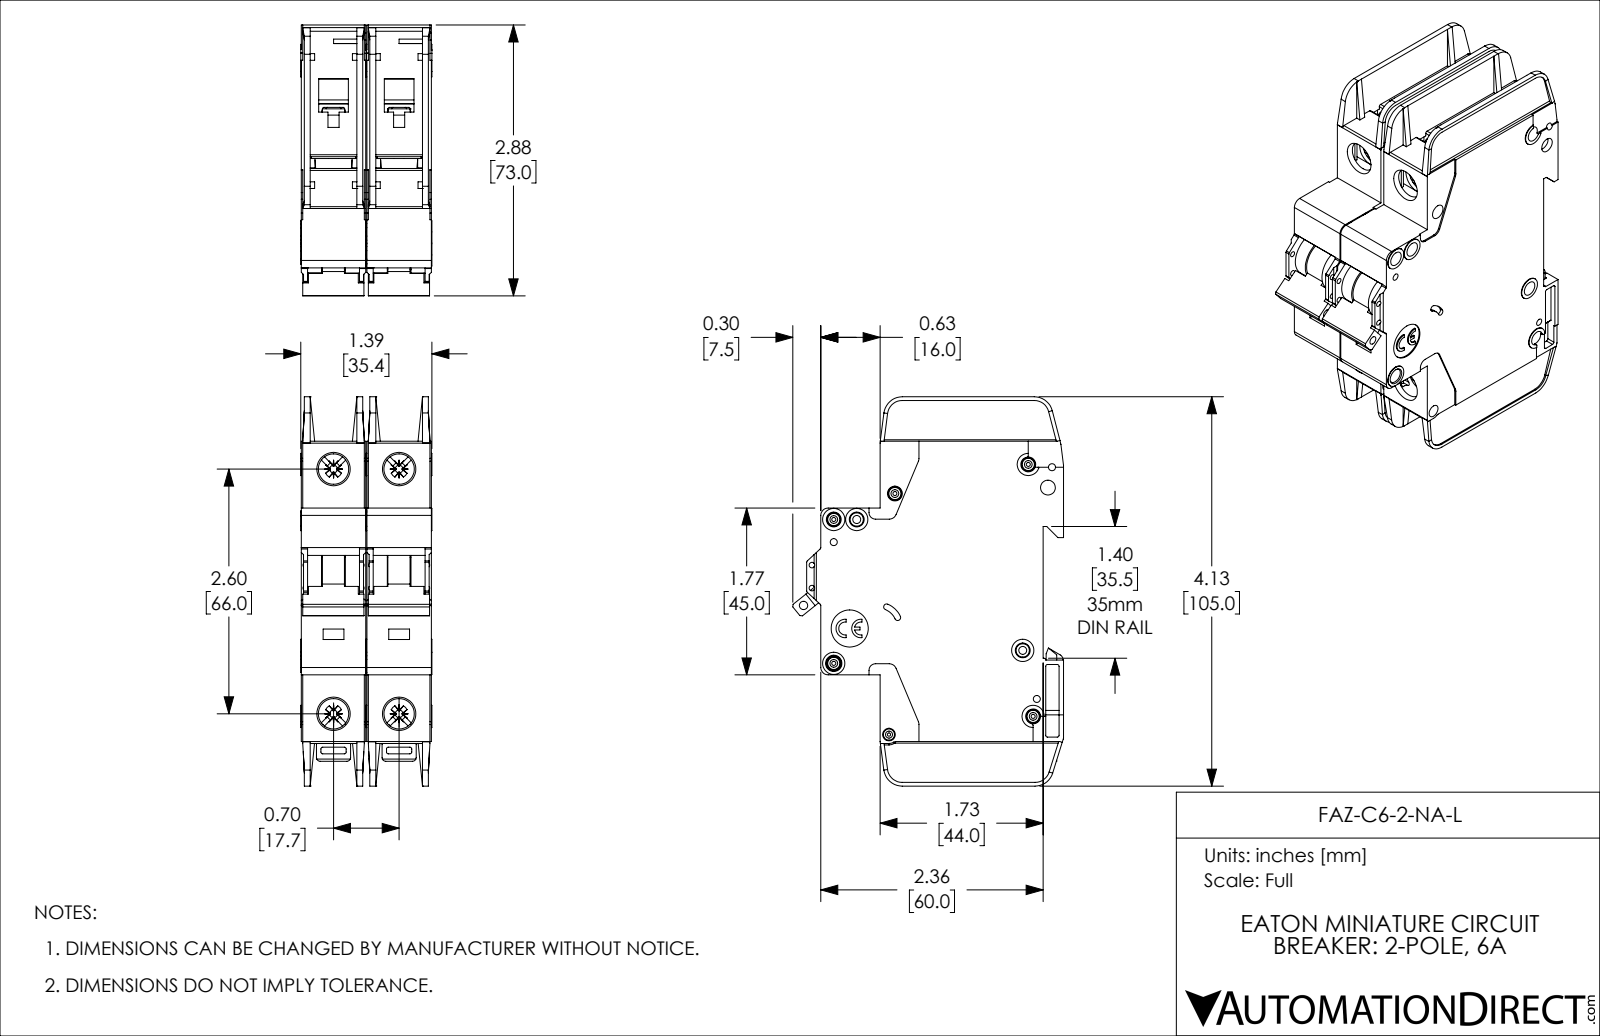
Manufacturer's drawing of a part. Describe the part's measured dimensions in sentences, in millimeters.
The part is named "FAZ-C6-2-NA-L". Its 3-D file was written by "SolidWorks 2019 (AUTOMOTIVE_DESIGN)". It is 2 solids with 2254 faces: 1342 planar, 714 cylindrical and 198 other. Overall it measures 105 by 73.1 by 35.4 millimeters. Its volume is 153 500 cubic millimeters and its surface area 52 910 square millimeters. Round holes: 8 of diameter 4, 5 of diameter 1.1, 4 of diameter 1.9, 4 of diameter 8.2, 2 of diameter 1.5, 2 of diameter 2.2, 1 of diameter 0.9, 1 of diameter 2.3, 1 of diameter 2.5, 1 of diameter 3.4, 1 of diameter 10. Round bosses or shafts: 5 of diameter 3.3, 4 of diameter 6, 3 of diameter 3, 2 of diameter 2.5. Partial cylindrical surfaces (rounded edges, fillets, slot ends): 57 of radius 0.5, 20 of radius 0.4, 14 of radius 1, 10 of radius 2, 8 of radius 1.1, 5 of radius 0.2, 5 of radius 5, 4 of radius 0.3. The main face-to-face distances are 17.7, 1.2, 17.4, 15, 2.4, 16.2, 13.8, 35.1, 18.9, 16.5. The hole center spacings are 6.2, 13.6, 17.7, 22.1, 66, 68.3, 4.8, 5.1.
